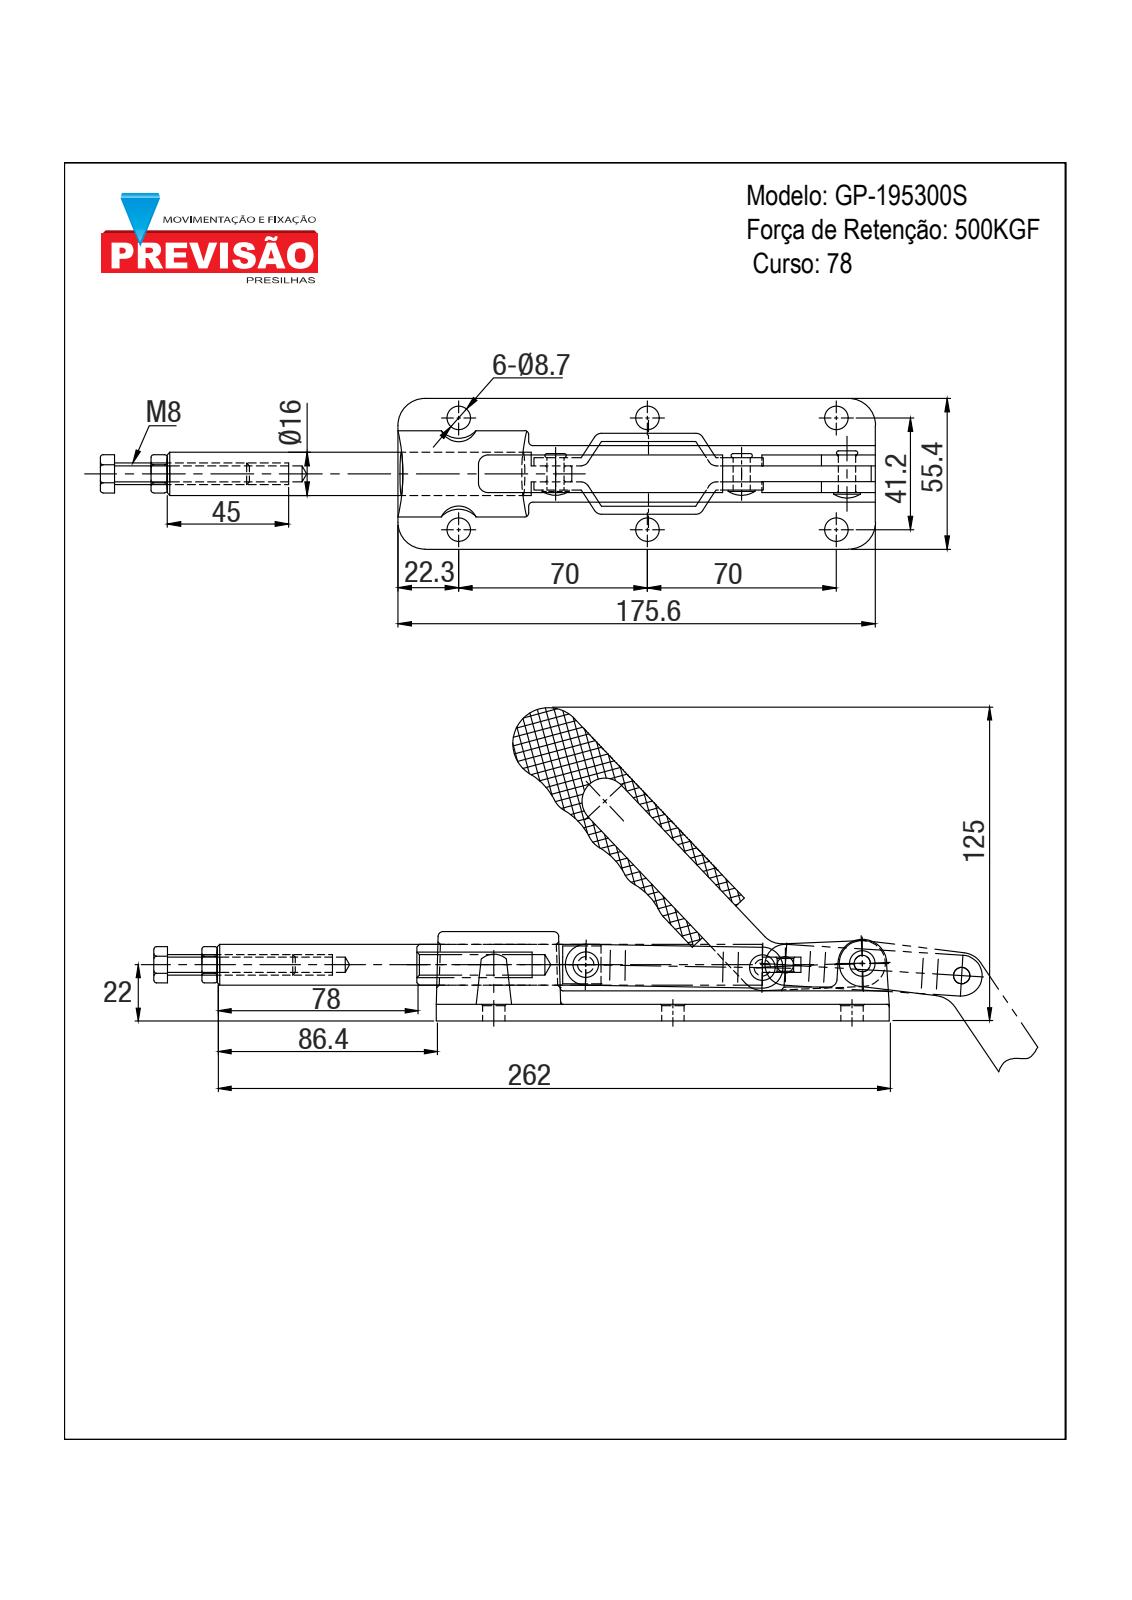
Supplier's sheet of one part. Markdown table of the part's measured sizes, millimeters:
| quantity | value |
| --- | --- |
| part name | CH-36330ML |
| STEP written by | SolidWorks 2015 (CONFIG_CONTROL_DESIGN) |
| units | millimeters |
| bodies | 11 solids, 1313 faces (443 planar, 478 cylindrical, 392 other) |
| overall size | 286.9 × 119.54 × 55.4 |
| volume | 186 546 mm³ |
| surface area | 72 757 mm² |
| round holes (diameter × count) | 8.7 × 6, 6.4 × 3, 2.1 × 1, 6.5 × 1, 7 × 1, 16 × 1 |
| round bosses / shafts (diameter × count) | 9.42 × 2, 8 × 1, 1.99 × 1 |
| partial cylindrical surfaces (radius × count) | 0.25 × 84, 3 × 9, 1 × 8, 10 × 8, 25.91 × 8, 3.5 × 7, 2 × 4, 8 × 4 |
| main face-to-face distances | 6.5, 4, 5.9, 10, 9, 18, 6, 11.8, 5.3, 3 |
| hole center spacings | 70, 81.22, 41.2, 140, 145.94, 27.53, 39.1, 41.73 |
